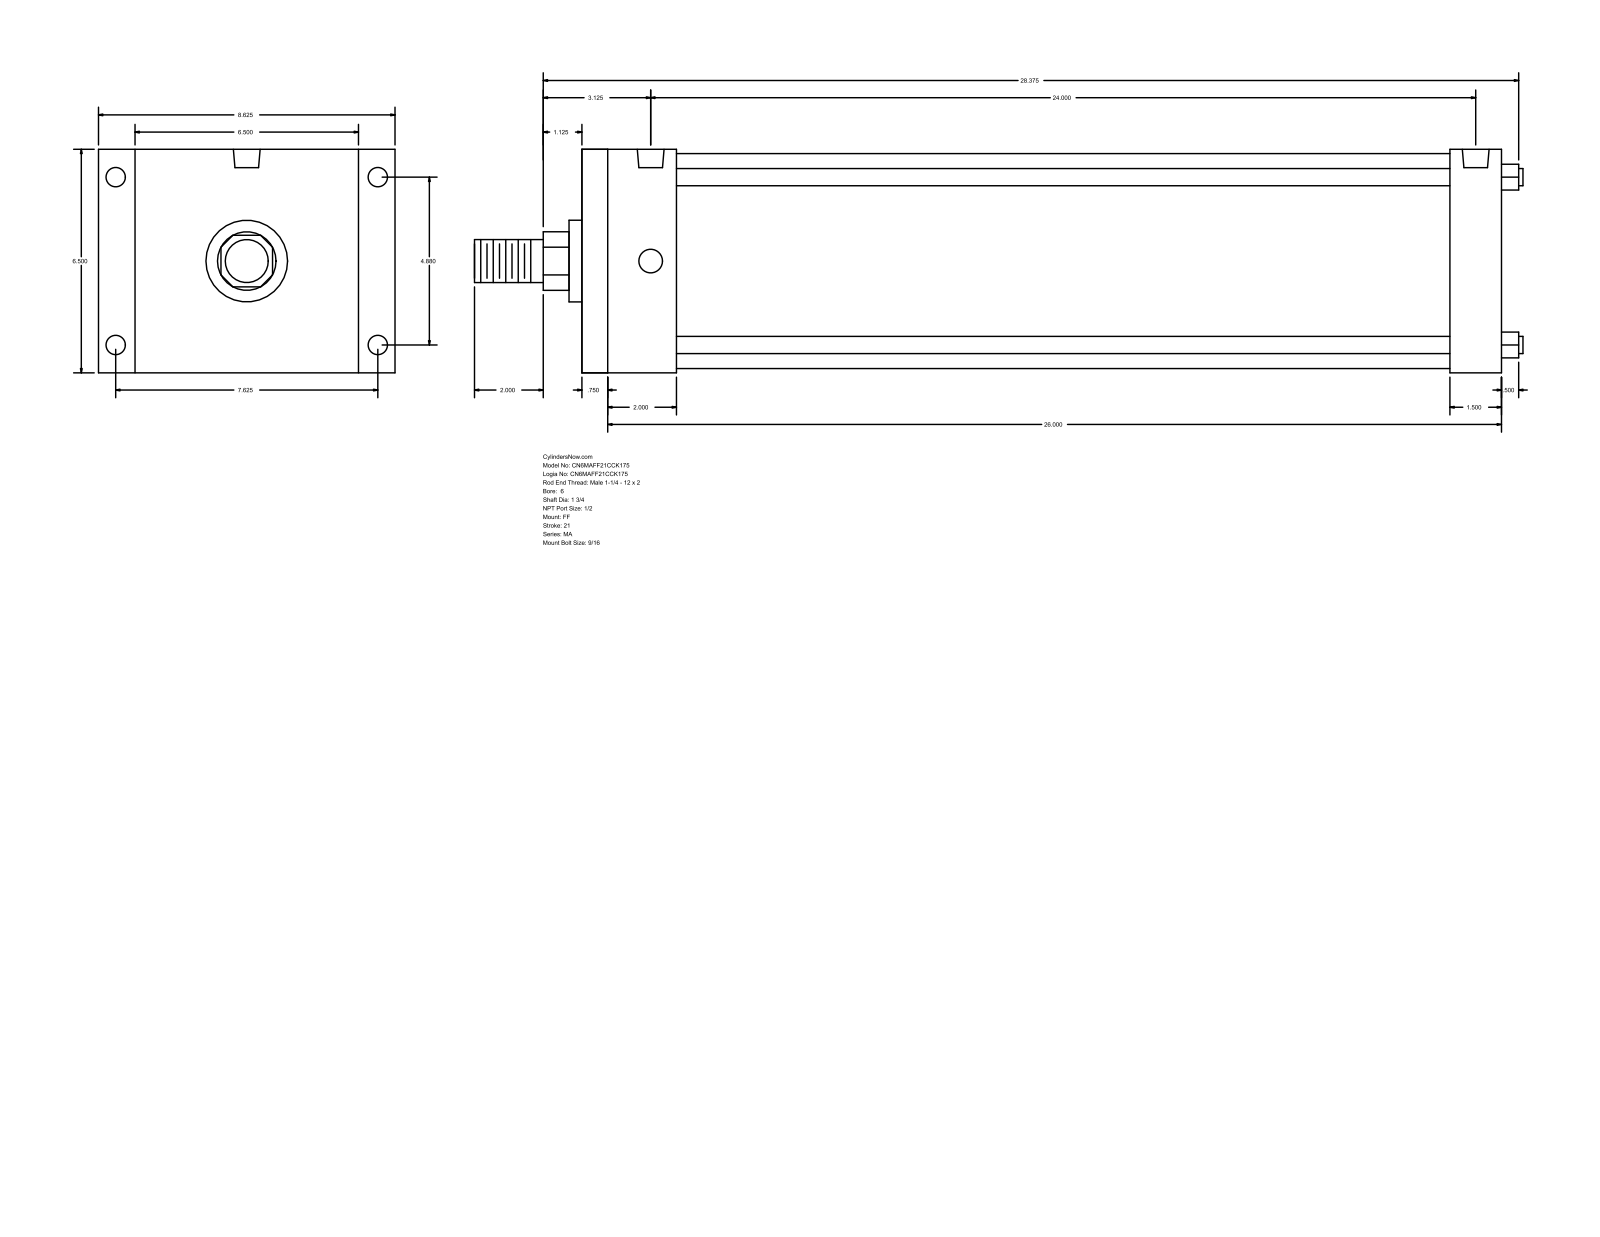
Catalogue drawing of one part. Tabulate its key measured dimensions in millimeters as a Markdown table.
| quantity | value |
| --- | --- |
| part name | MA_FF__0600_1.75 |
| STEP written by | GSSL Pune (CONFIG_CONTROL_DESIGN) |
| units | millimeters |
| bodies | 0 solids, 92 faces (64 planar, 28 cylindrical, 0 other) |
| overall size | 774.7 × 219.07 × 165.1 |
| round holes (diameter × count) | 14.29 × 4, 17.46 × 4, 19.77 × 2 |
| round bosses / shafts (diameter × count) | 12.7 × 4, 158.75 × 1, 60.33 × 1, 44.45 × 1, 31.75 × 1 |
| partial cylindrical surfaces (radius × count) | 21.63 × 1 |
| main face-to-face distances | 165.1, 679.45, 19.05, 660.4, 69.85, 38.1, 50.8, 609.6, 641.35, 622.3 |
| hole center spacings | 123.96, 193.68, 229.95, 609.6 |
